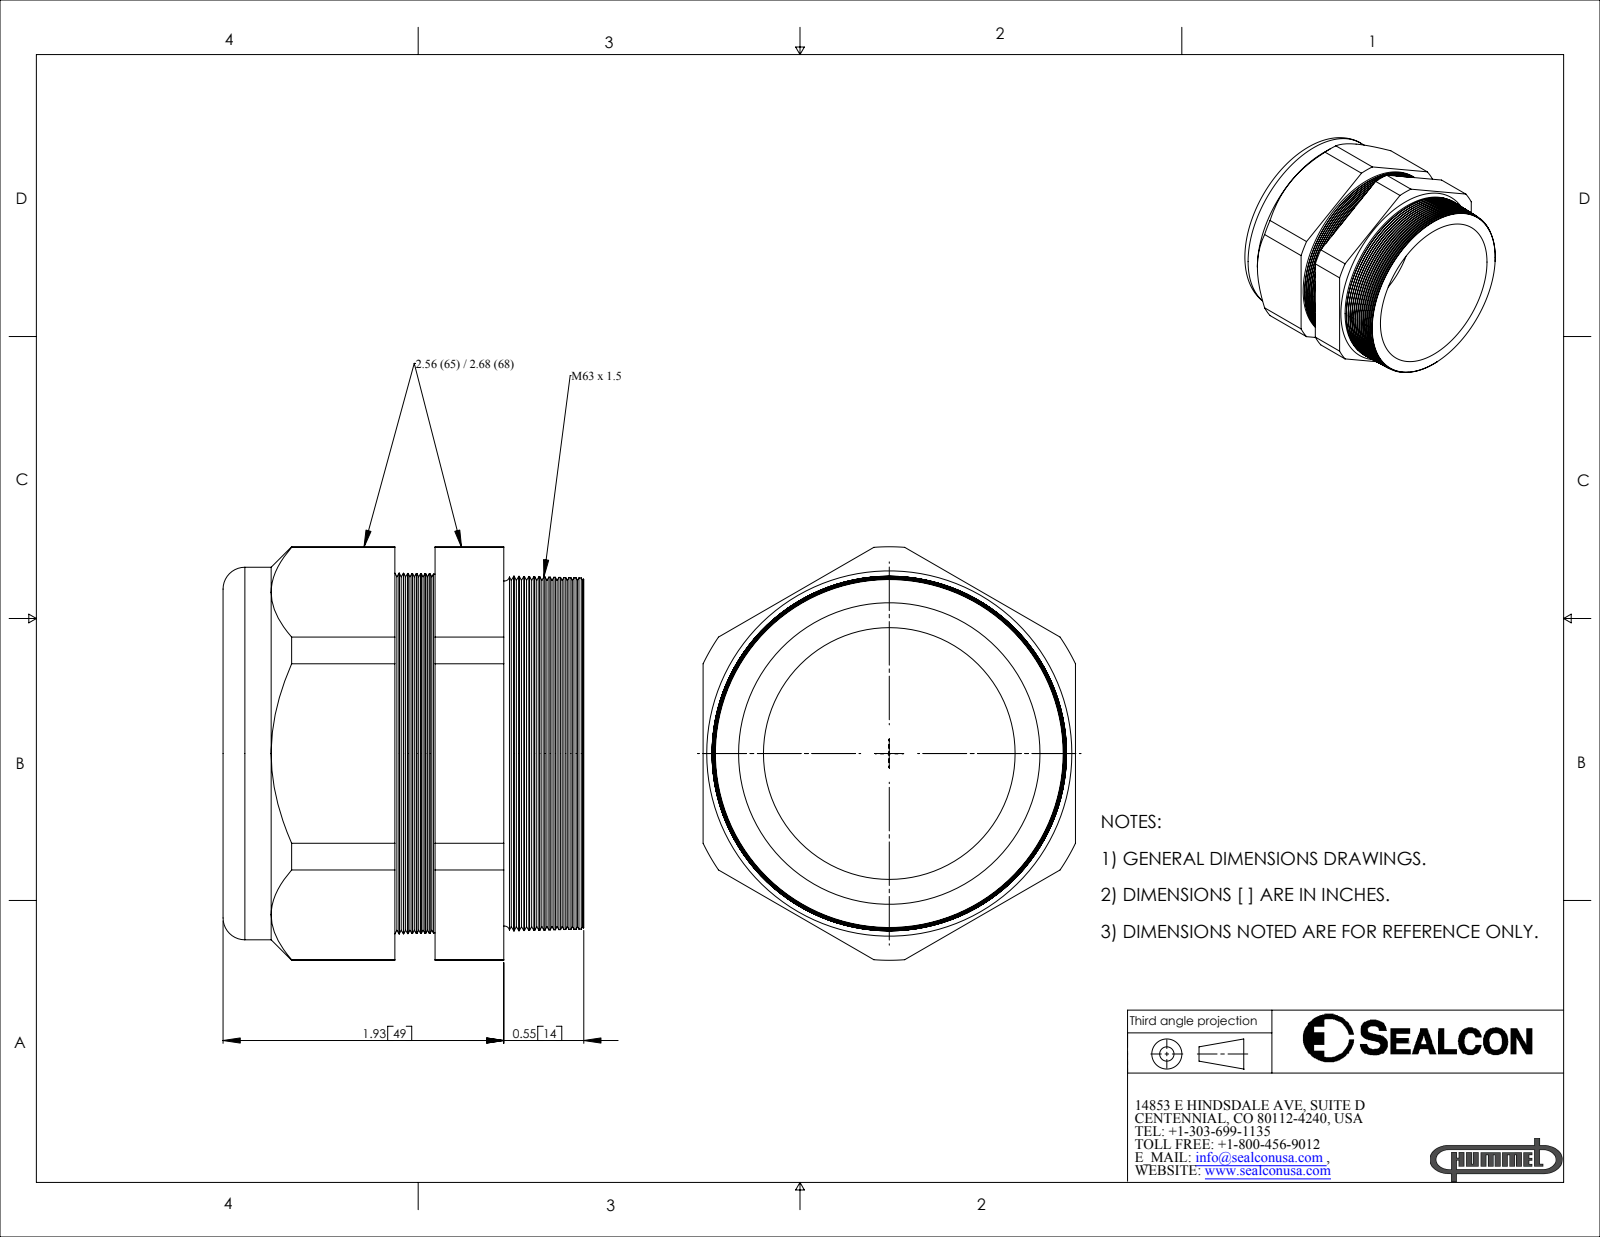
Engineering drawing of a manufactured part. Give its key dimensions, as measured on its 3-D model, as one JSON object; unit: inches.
{"part_name": "CD63MP-GY", "step_written_by": "SolidWorks 2007 (CONFIG_CONTROL_DESIGN)", "units": "inches", "bodies": {"solids": 2, "faces": 198, "planar": 20, "cylindrical": 20, "other": 158}, "overall_size": [2.842, 2.56, 2.48], "volume_in3": 7.552, "surface_area_in2": 53.64, "round_holes": [[1.71, 1], [1.73, 1]], "round_bosses_or_shafts": [[2.56, 1]], "partial_cylinders_radius": [[1.421, 1]], "face_to_face_distances": [2.56, 0.48, 0.02, 0.5, 2.48, 2.46, 1.98, 1.458, 1.438, 0.958]}
